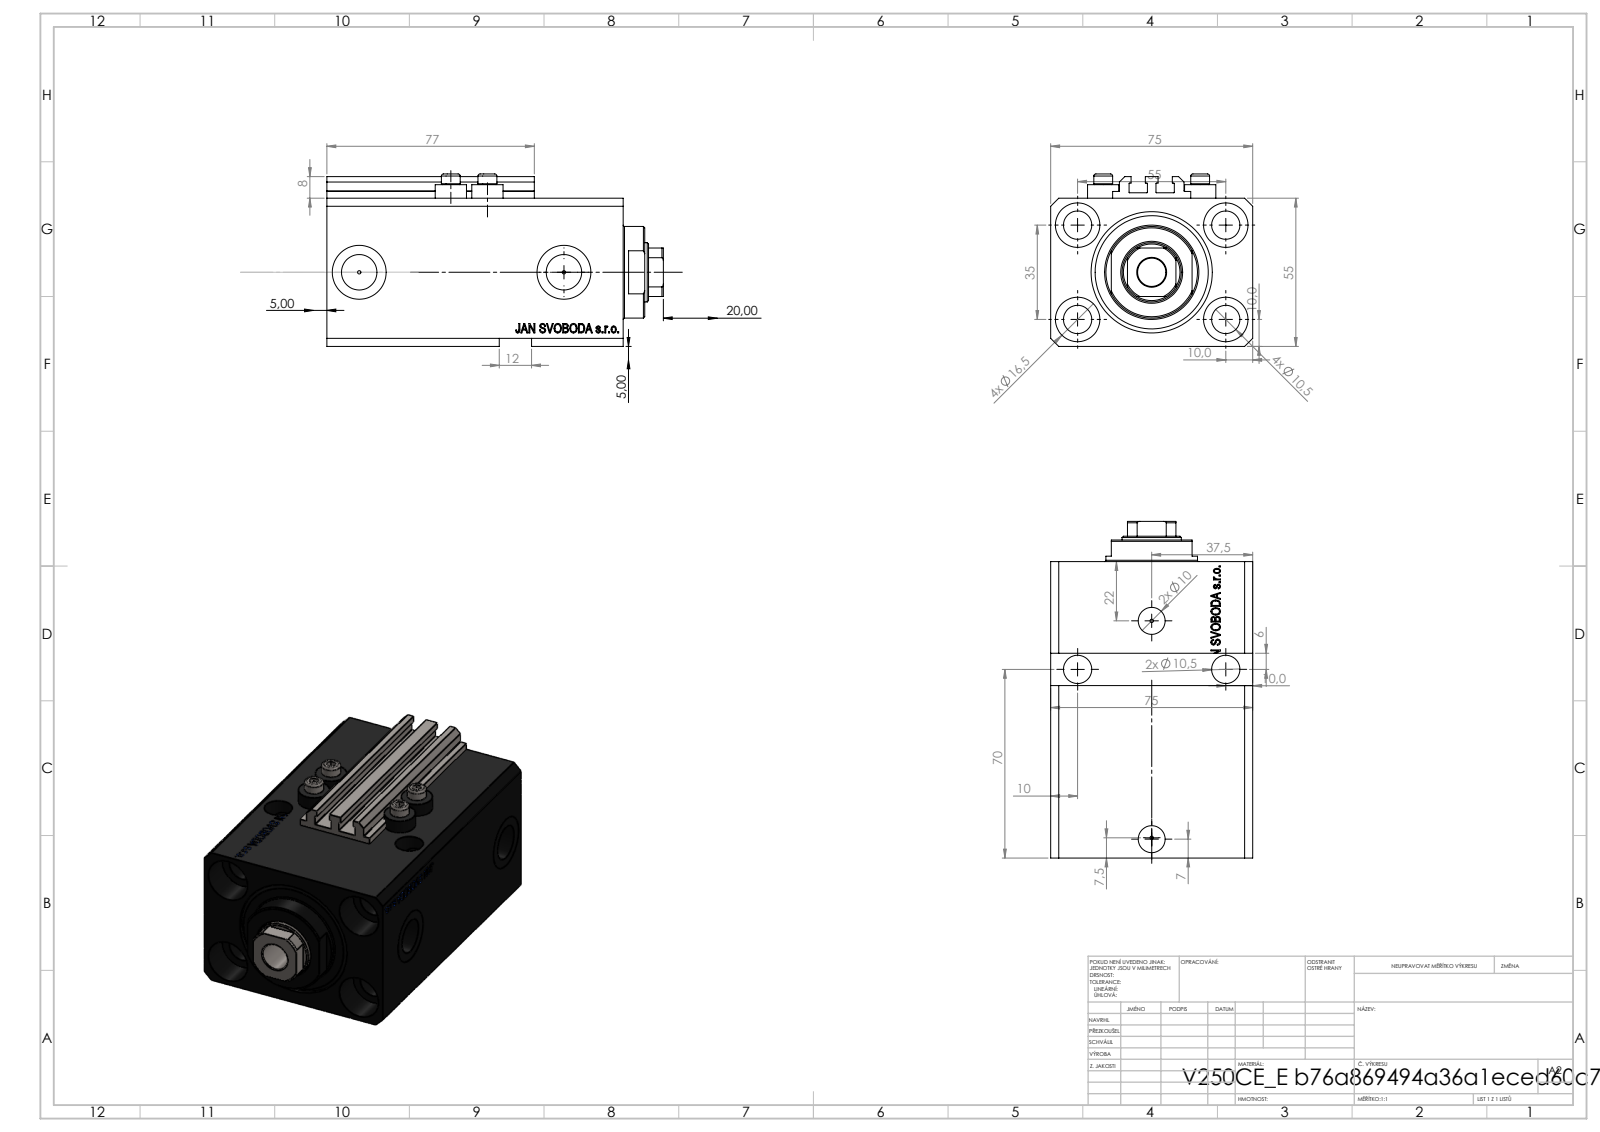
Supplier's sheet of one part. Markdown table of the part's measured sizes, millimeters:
| quantity | value |
| --- | --- |
| part name | ALLEN BOLT V250CE; V250CE_VC_E; V250CE_E_Body; V250CE_C_VCP |
| STEP written by | SolidWorks 2019 (CONFIG_CONTROL_DESIGN) |
| units | millimeters |
| bodies | 8 solids, 1100 faces (518 planar, 158 cylindrical, 424 other) |
| overall size | 125 × 75 × 64 |
| volume | 377 718 mm³ |
| surface area | 96 791 mm² |
| round holes (diameter × count) | 10.5 × 9, 1.25 × 4, 4 × 4, 16.5 × 4, 10 × 2, 13.16 × 2, 20 × 2, 22 × 1, 32 × 1, 45 × 1 |
| round bosses / shafts (diameter × count) | 11.6 × 4, 7 × 4, 34 × 1 |
| partial cylindrical surfaces (radius × count) | 0.2 × 10, 10.5 × 1 |
| main face-to-face distances | 55, 75, 15, 110, 95, 9.9, 3, 85.1, 100.1, 57 |
| hole center spacings | 32.6, 32.87, 55, 68.74, 13.6, 14.09, 23.05, 25.81 |
